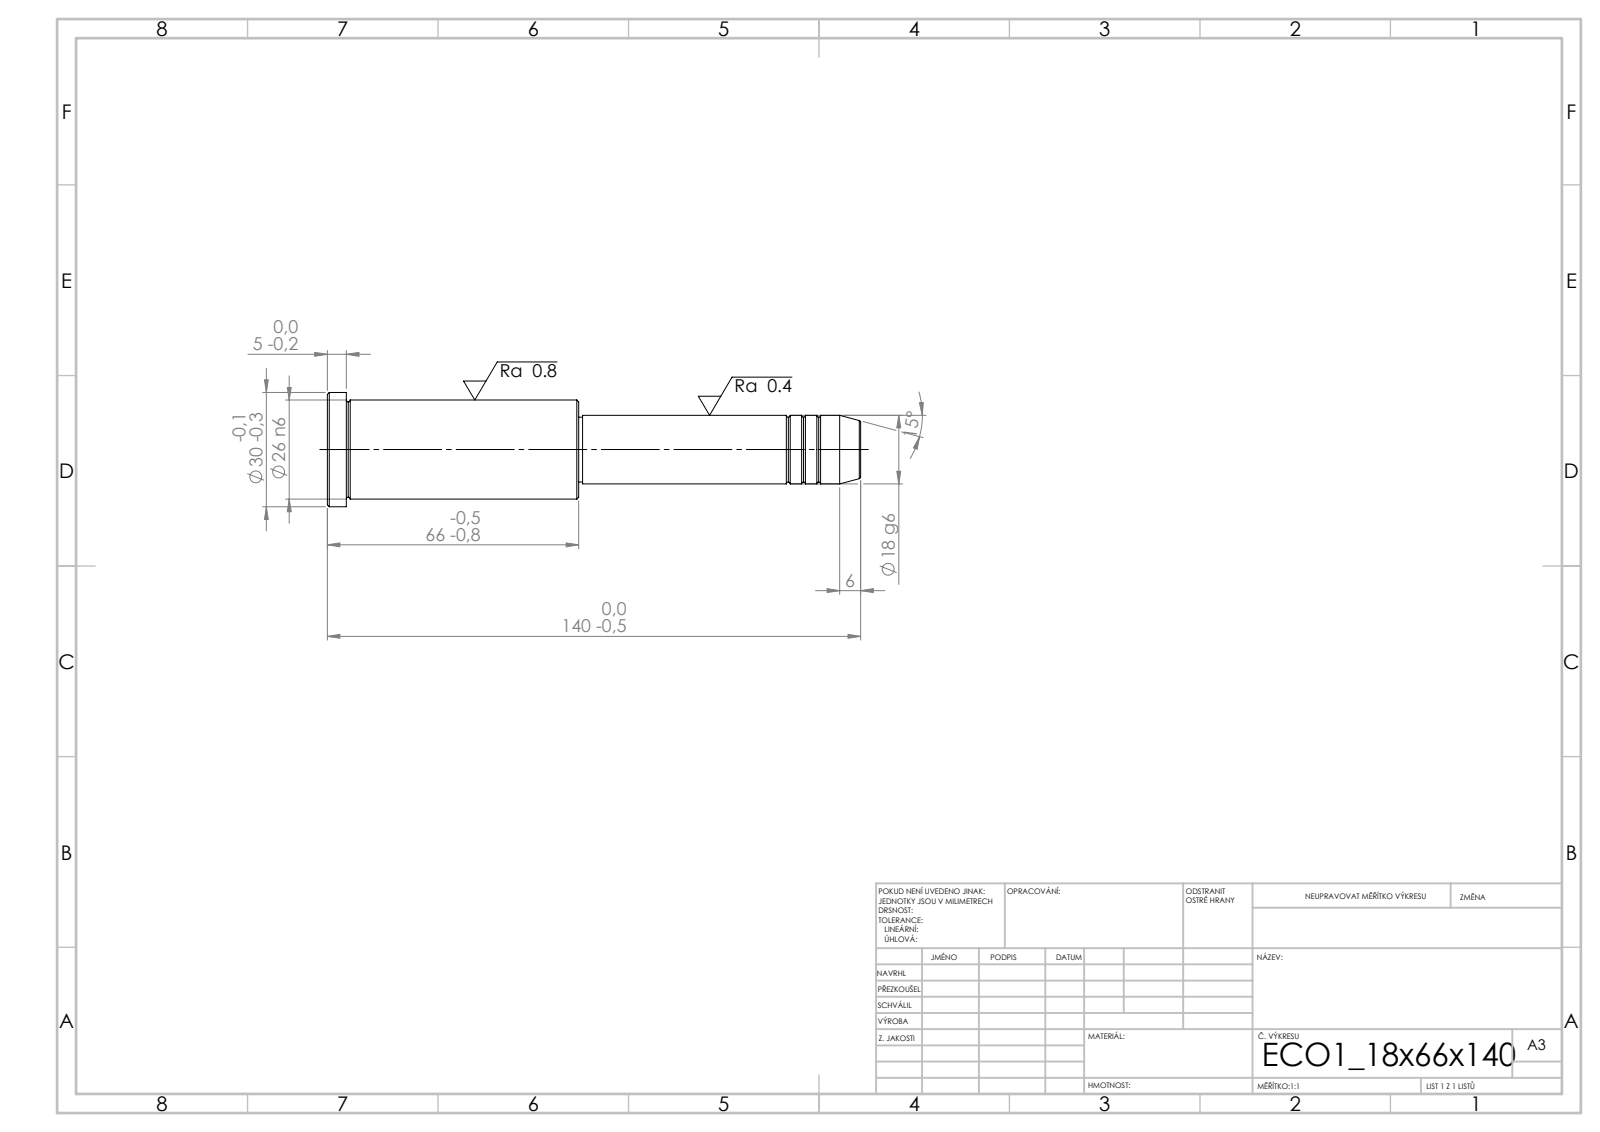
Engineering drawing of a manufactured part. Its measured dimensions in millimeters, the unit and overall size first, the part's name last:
Units: millimetres
Overall size (bounding box): 140 × 30 × 30
Round bosses / shafts (diameter × count): ⌀30 ×1, ⌀26 ×1, ⌀18 ×1, ⌀17 ×1
Main face-to-face distances: 66, 61, 5, 74, 135, 140, 73, 1, 62, 67
Volume: 54 388 mm³ · Surface area: 11 085 mm²
Bodies: 1 solid, 43 faces (5 planar, 14 cylindrical, 24 other)
STEP written by: SolidWorks 2019 (CONFIG_CONTROL_DESIGN)
